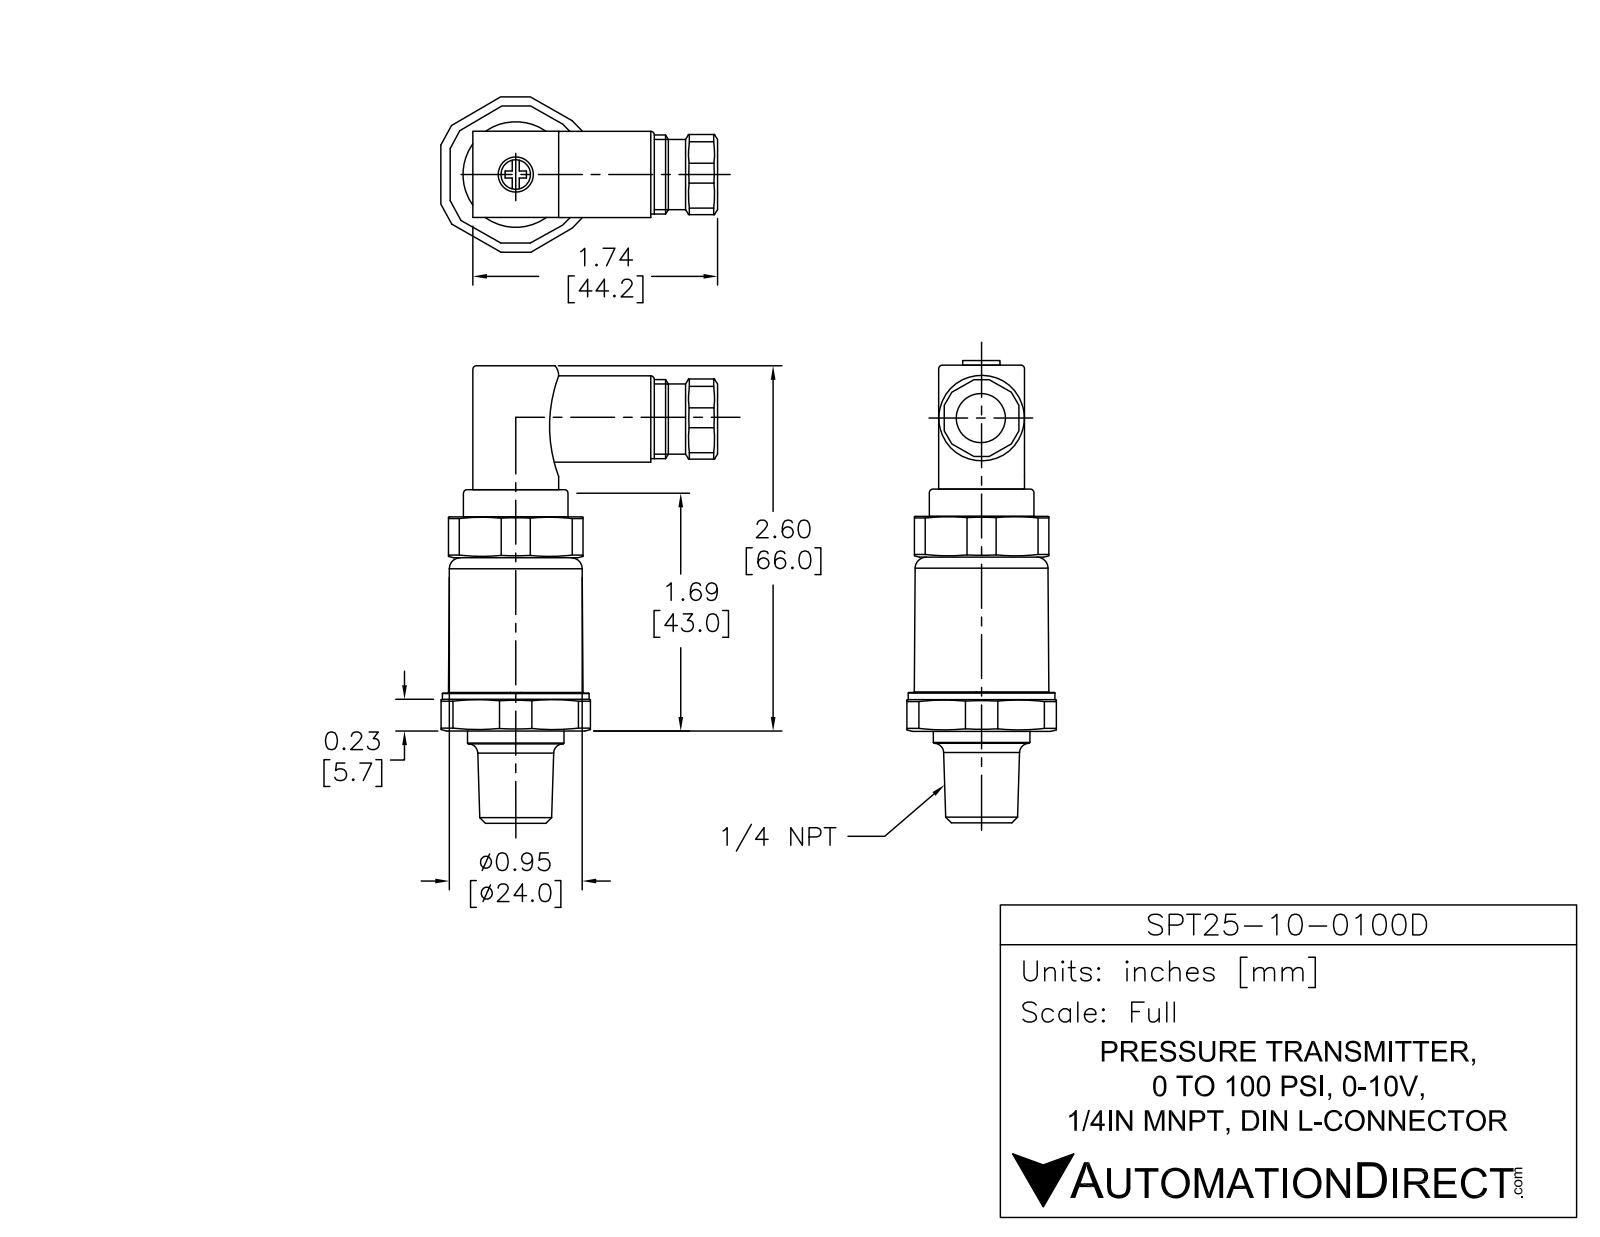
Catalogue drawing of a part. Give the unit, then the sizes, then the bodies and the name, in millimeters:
Units: millimetres
Overall size (bounding box): 81.25 × 38.01 × 35.71
Round holes (diameter × count): ⌀1 ×1, ⌀3.3 ×1, ⌀7 ×1, ⌀8 ×1
Round bosses / shafts (diameter × count): ⌀26.75 ×1, ⌀24 ×1, ⌀17.5 ×1, ⌀15 ×1, ⌀14 ×1, ⌀11 ×1
Partial cylindrical surfaces — rounded edges, fillets, slot ends (radius × count): R1.5 ×8, R1.15 ×4, R2.25 ×4, R2 ×3, R1.15 ×1, R1.17 ×1, R14.5 ×1
Main face-to-face distances: 1.5, 29.5, 31, 15.75, 0.35, 15.4, 6.75, 37.75, 36.25, 5
Hole centre spacings: 1.33
Volume: 27 893 mm³ · Surface area: 10 133 mm²
Bodies: 5 solids, 200 faces (96 planar, 87 cylindrical, 17 other)
Part name (STEP PRODUCT): SPT25-10-0100D
STEP written by: SolidWorks 2013 (AUTOMOTIVE_DESIGN)
